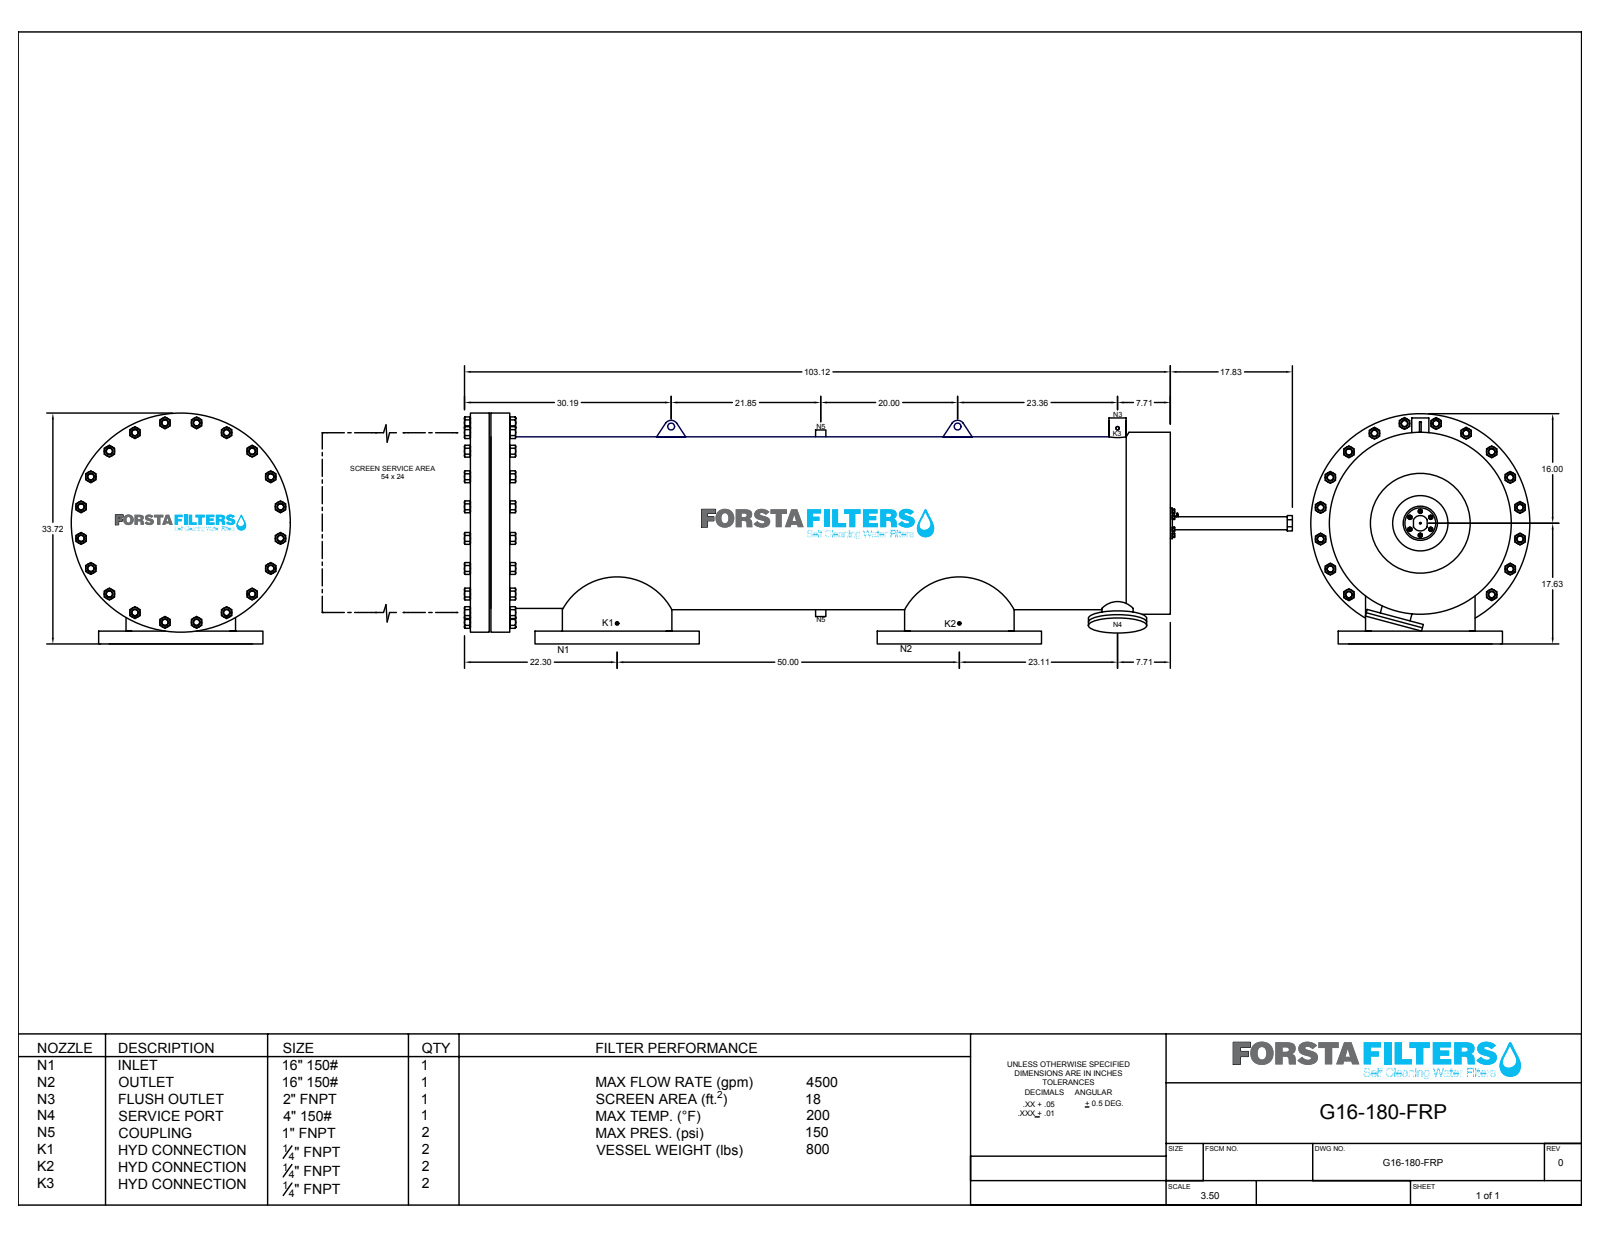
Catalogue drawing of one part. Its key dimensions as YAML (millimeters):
part_name: "G16-FRP-180"
step_written_by: "SolidWorks 2018 (CONFIG_CONTROL_DESIGN)"
units: millimeters
bodies: {solids: 27, faces: 894, planar: 440, cylindrical: 450, other: 4}
overall_size: [3067.3, 854.2, 845.1]
volume: 92690000
surface_area: 15080000
round_holes:
  - {diameter: 28.4, count: 24}
  - {diameter: 25.4, count: 23}
  - {diameter: 19.1, count: 16}
  - {diameter: 9.5, count: 6}
  - {diameter: 6.4, count: 4}
  - {diameter: 101.6, count: 2}
  - {diameter: 406.4, count: 2}
  - {diameter: 33.5, count: 1}
  - {diameter: 50.8, count: 1}
  - {diameter: 626.6, count: 1}
  - {diameter: 660.3, count: 1}
round_bosses_or_shafts:
  - {diameter: 16.4, count: 3}
  - {diameter: 596.9, count: 2}
  - {diameter: 416.4, count: 2}
  - {diameter: 228.6, count: 2}
  - {diameter: 111.6, count: 2}
  - {diameter: 812.8, count: 1}
  - {diameter: 670.3, count: 1}
  - {diameter: 636.6, count: 1}
partial_cylinders:
  - {radius: 25.4, count: 2}
  - {radius: 28.6, count: 1}
face_to_face_distances: [69.9, 76.2, 6.4, 2597.3, 2527.5, 2521.1, 2592.3, 2522.4, 2516.1, 5]
hole_center_spacings: [269.9, 117.2, 231.5, 269.9, 340.2, 440.4, 467.4, 521.4]
